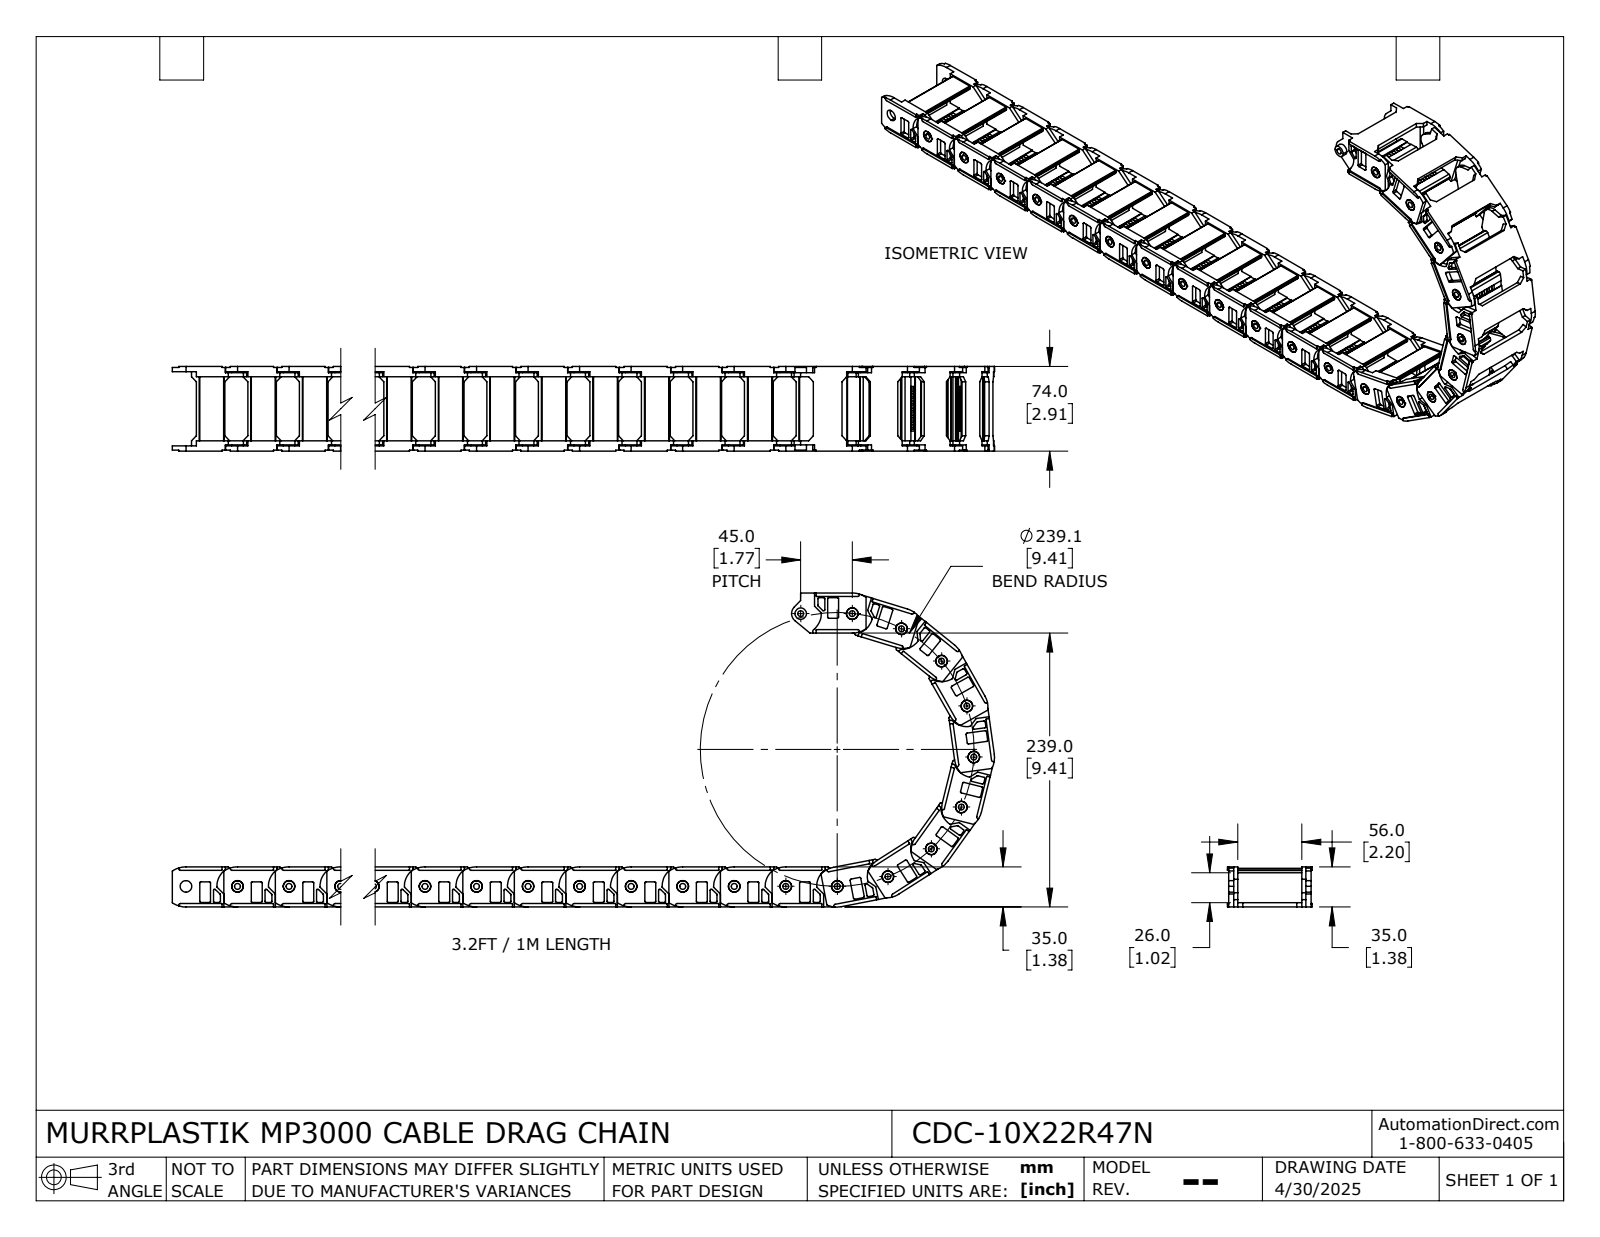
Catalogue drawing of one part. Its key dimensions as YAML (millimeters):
part_name: "CDC-10X22R47N"
step_written_by: "SolidWorks 2024 (AUTOMOTIVE_DESIGN)"
units: millimeters
bodies: {solids: 22, faces: 4224, planar: 3124, cylindrical: 1100, other: 0}
overall_size: [734.23, 274.07, 74]
volume: 657728
surface_area: 397693
round_holes:
  - {diameter: 5.1, count: 22}
  - {diameter: 10.1, count: 22}
round_bosses_or_shafts:
  - {diameter: 10, count: 22}
partial_cylinders:
  - {radius: 1, count: 176}
  - {radius: 0.5, count: 88}
  - {radius: 1.5, count: 44}
  - {radius: 2, count: 44}
  - {radius: 21, count: 44}
  - {radius: 2.8, count: 22}
  - {radius: 8, count: 22}
  - {radius: 18, count: 22}
face_to_face_distances: [64, 8, 4, 3.7, 68.3, 4.3, 60.3, 3.5, 56, 0.8]
hole_center_spacings: [45, 90, 135, 180, 225, 270, 315, 44.96]
